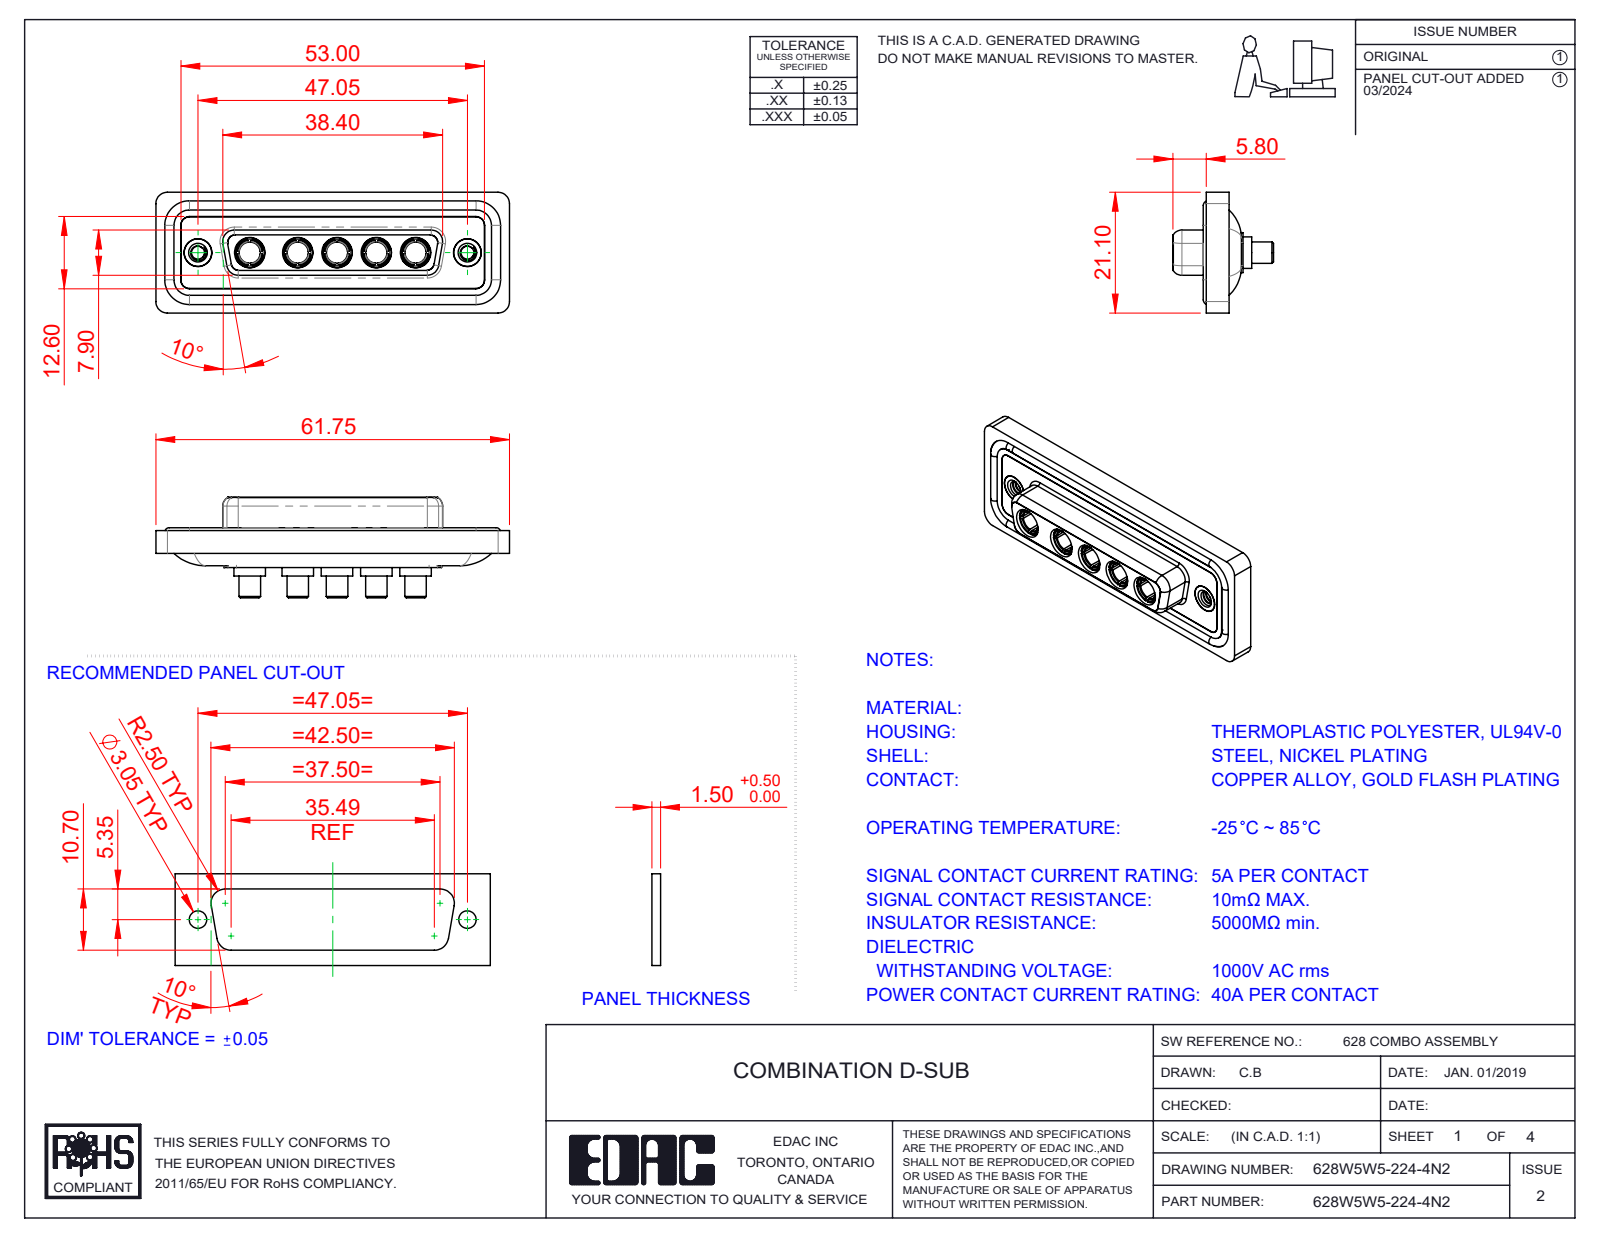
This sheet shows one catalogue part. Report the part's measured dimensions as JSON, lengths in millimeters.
{"part_name": "628W5W5-224-4N2; 628Combo Shell Rear_25 Contacts; 628Combo Threaded Rivet_2; 628Combo Housing_5W5 (+3 more)", "step_written_by": "SolidWorks 2023 (CONFIG_CONTROL_DESIGN)", "units": "millimeters", "bodies": {"solids": 17, "faces": 756, "planar": 250, "cylindrical": 303, "other": 203}, "overall_size": [61.75, 21.1, 17.55], "volume_mm3": 8265, "surface_area_mm2": 13470, "round_holes": [[4.85, 7], [3.7, 5], [5.3, 5], [2.26, 2], [4, 2], [4.05, 2], [5, 2]], "round_bosses_or_shafts": [[5.5, 5], [5.2, 5], [4.96, 5], [4.75, 5], [3.75, 5], [1.6, 4], [4.95, 2], [4.8, 2]], "partial_cylinders_radius": [[1.5, 22], [2, 18], [1.35, 8], [1.6, 8], [2.1, 5], [0.25, 4], [0.5, 4], [0.6, 4]], "face_to_face_distances": [0.4, 1.8, 7.45, 5.65, 0.5, 7.05, 6.6, 1.6, 1.1, 2.9], "hole_center_spacings": [6.86, 9.04, 13.72, 38.01, 8.39, 15.25, 15.9, 17.43]}
